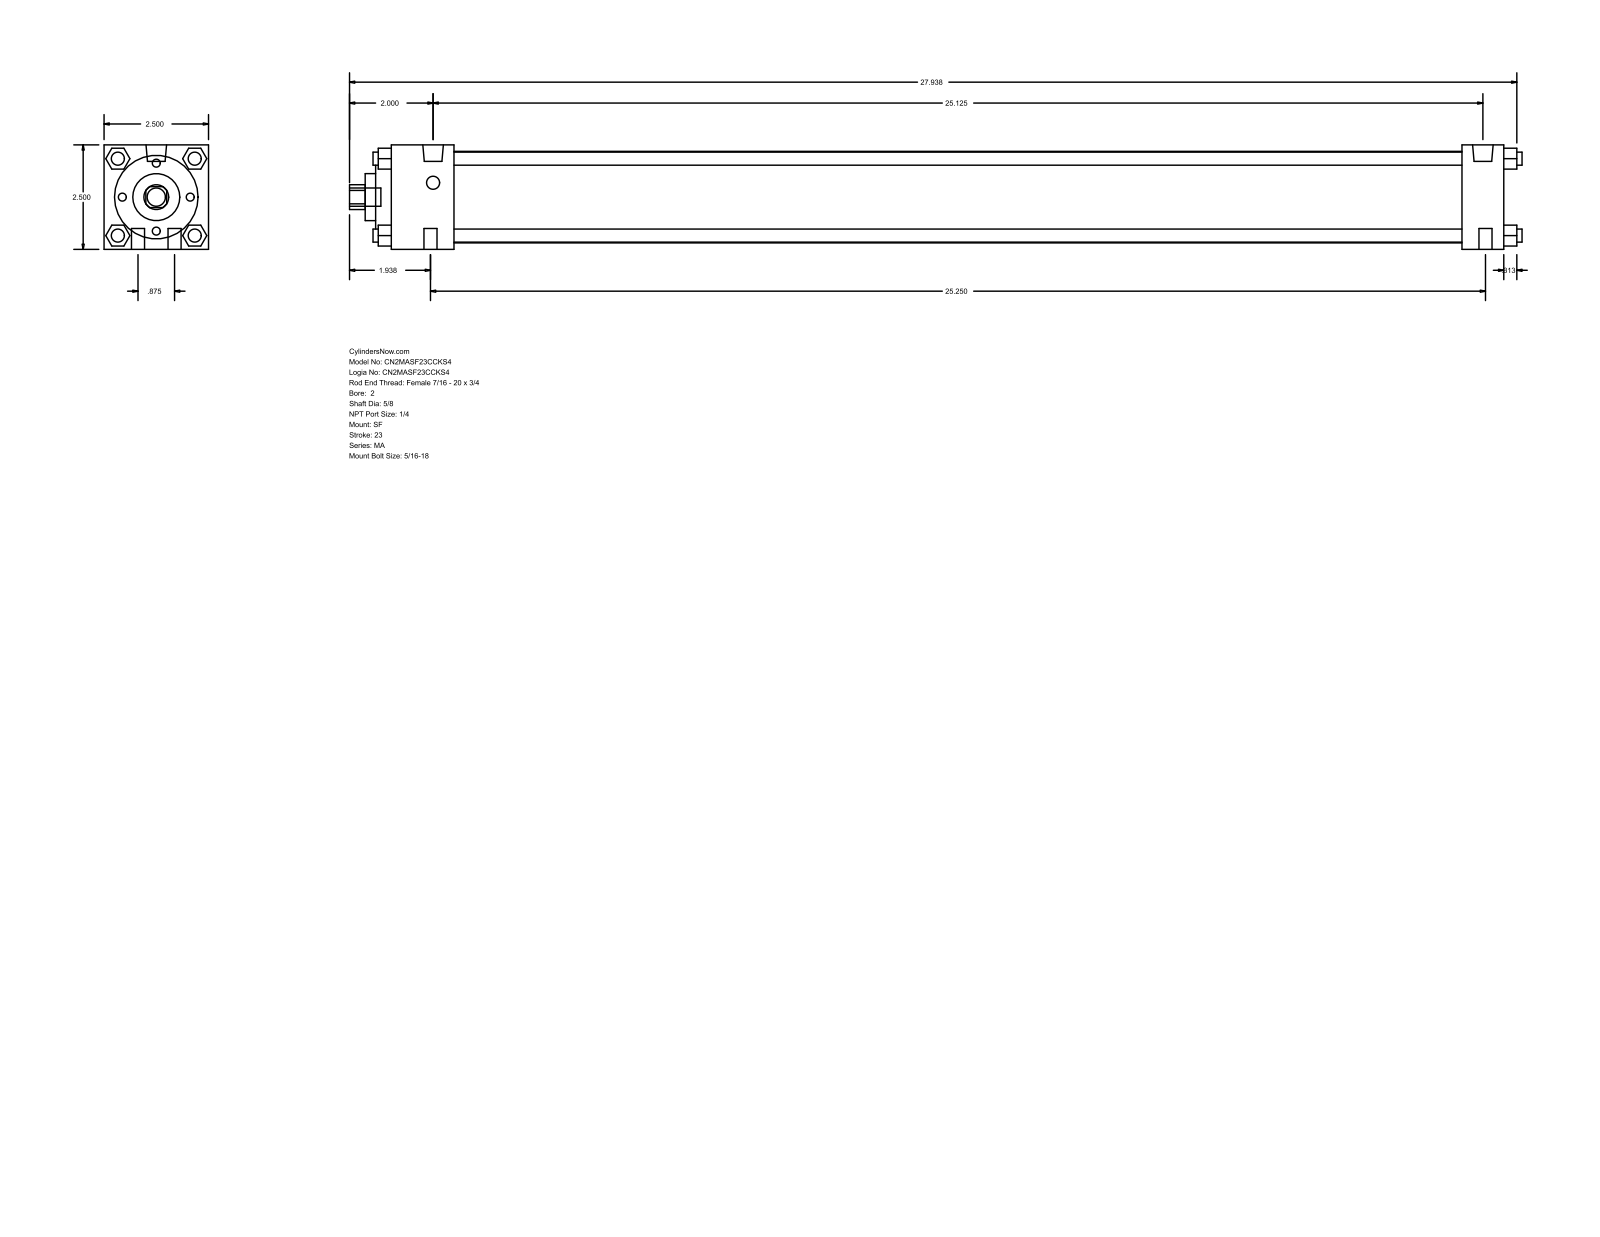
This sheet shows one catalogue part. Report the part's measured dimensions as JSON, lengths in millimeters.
{"part_name": "MA_SF__0200_0.625", "step_written_by": "GSSL Pune (CONFIG_CONTROL_DESIGN)", "units": "millimeters", "bodies": {"solids": 0, "faces": 126, "planar": 95, "cylindrical": 31, "other": 0}, "overall_size": [712.79, 63.5, 63.5], "round_holes": [[15.88, 1], [28.57, 1], [50.8, 1], [55.63, 1]], "round_bosses_or_shafts": [[7.94, 10], [12.49, 2], [11.11, 1]], "partial_cylinders_radius": [[7.54, 1]], "face_to_face_distances": [63.5, 12.7, 25.4, 38.1, 676.27, 9.52, 650.87, 612.77, 638.17, 47.62]}
